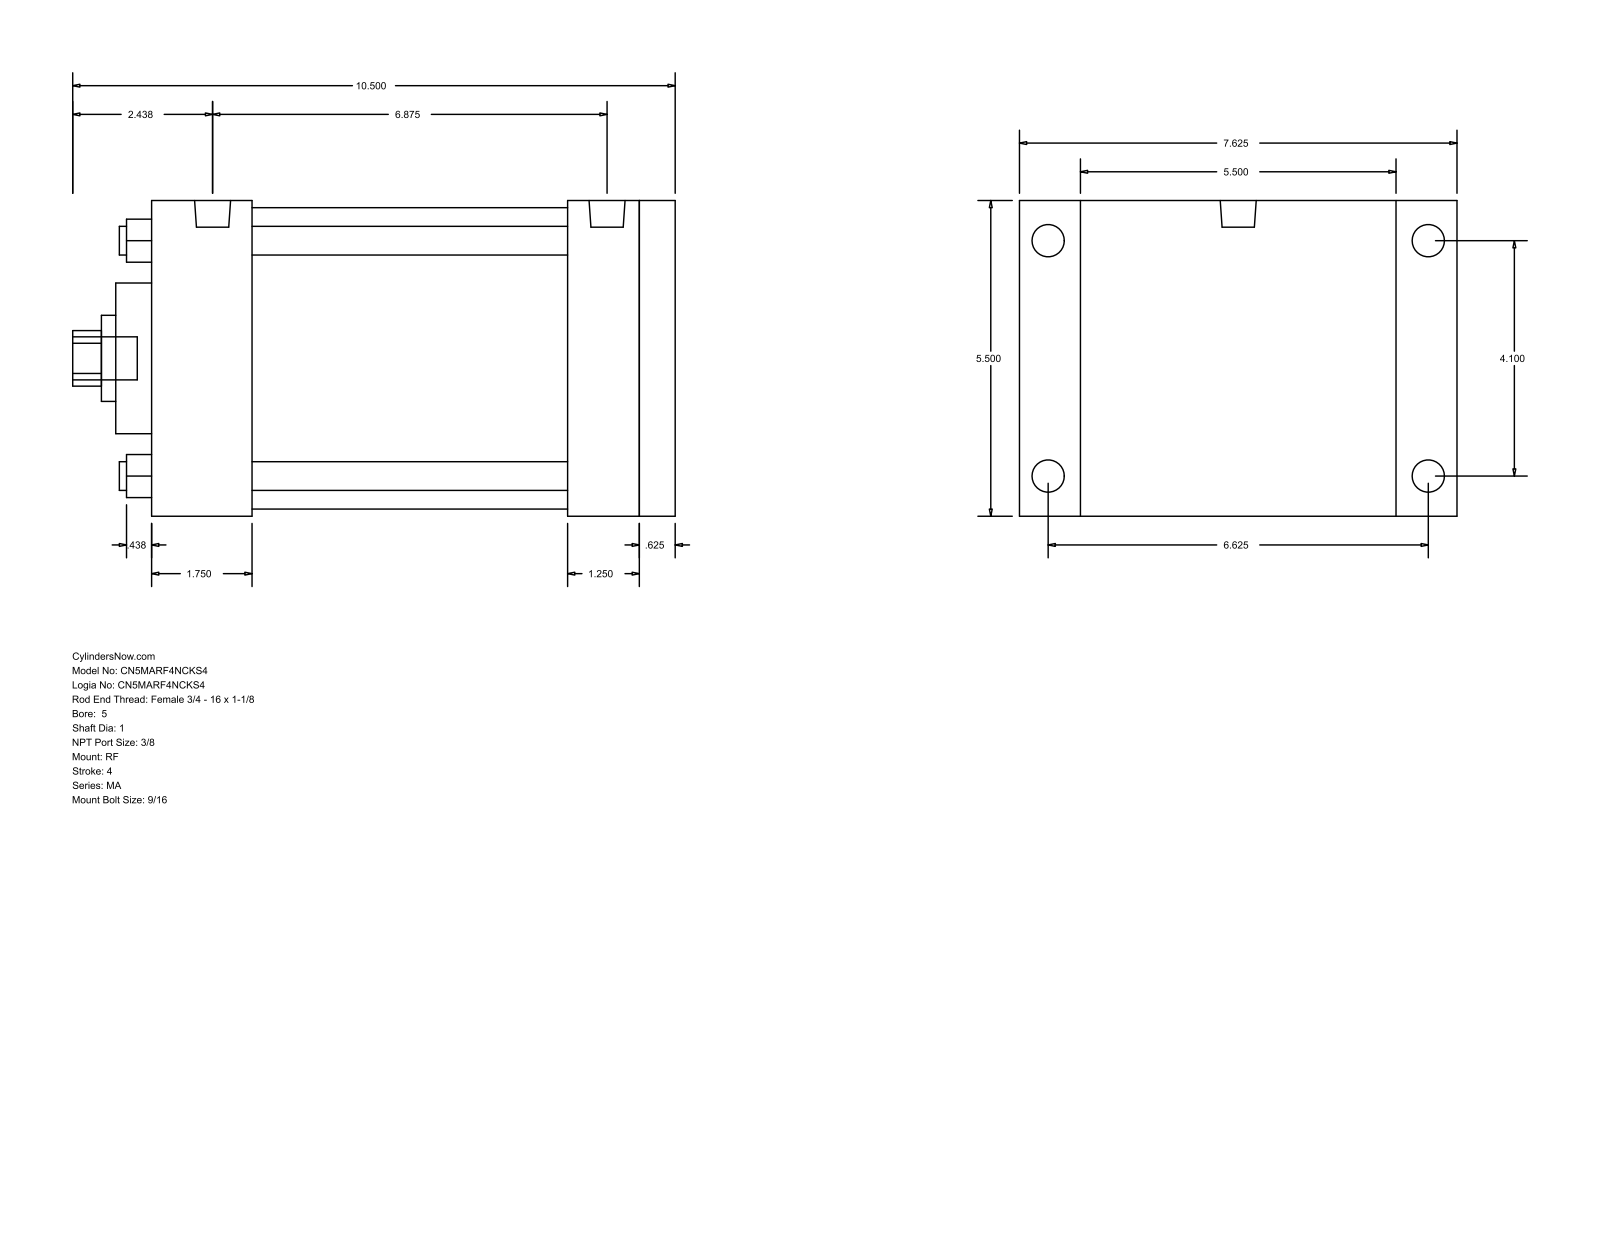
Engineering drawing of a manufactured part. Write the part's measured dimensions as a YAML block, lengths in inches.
part_name: "MA_RF__0500_1"
step_written_by: "GSSL Pune (CONFIG_CONTROL_DESIGN)"
units: inches
bodies: {solids: 0, faces: 94, planar: 65, cylindrical: 29, other: 0}
overall_size: [10.5, 7.625, 5.5]
round_holes:
  - {diameter: 0.5, count: 4}
  - {diameter: 1, count: 1}
  - {diameter: 1.5, count: 1}
  - {diameter: 2.625, count: 1}
  - {diameter: 5.25, count: 1}
round_bosses_or_shafts:
  - {diameter: 0.563, count: 4}
  - {diameter: 0.437, count: 4}
  - {diameter: 0.627, count: 2}
  - {diameter: 0.75, count: 1}
partial_cylinders:
  - {radius: 0.484, count: 1}
face_to_face_distances: [5.5, 9.125, 8.5, 0.625, 1.75, 6.75, 7.375, 7.25, 5.5, 1.25]
hole_center_spacings: [2.899, 4.1, 5.798]
